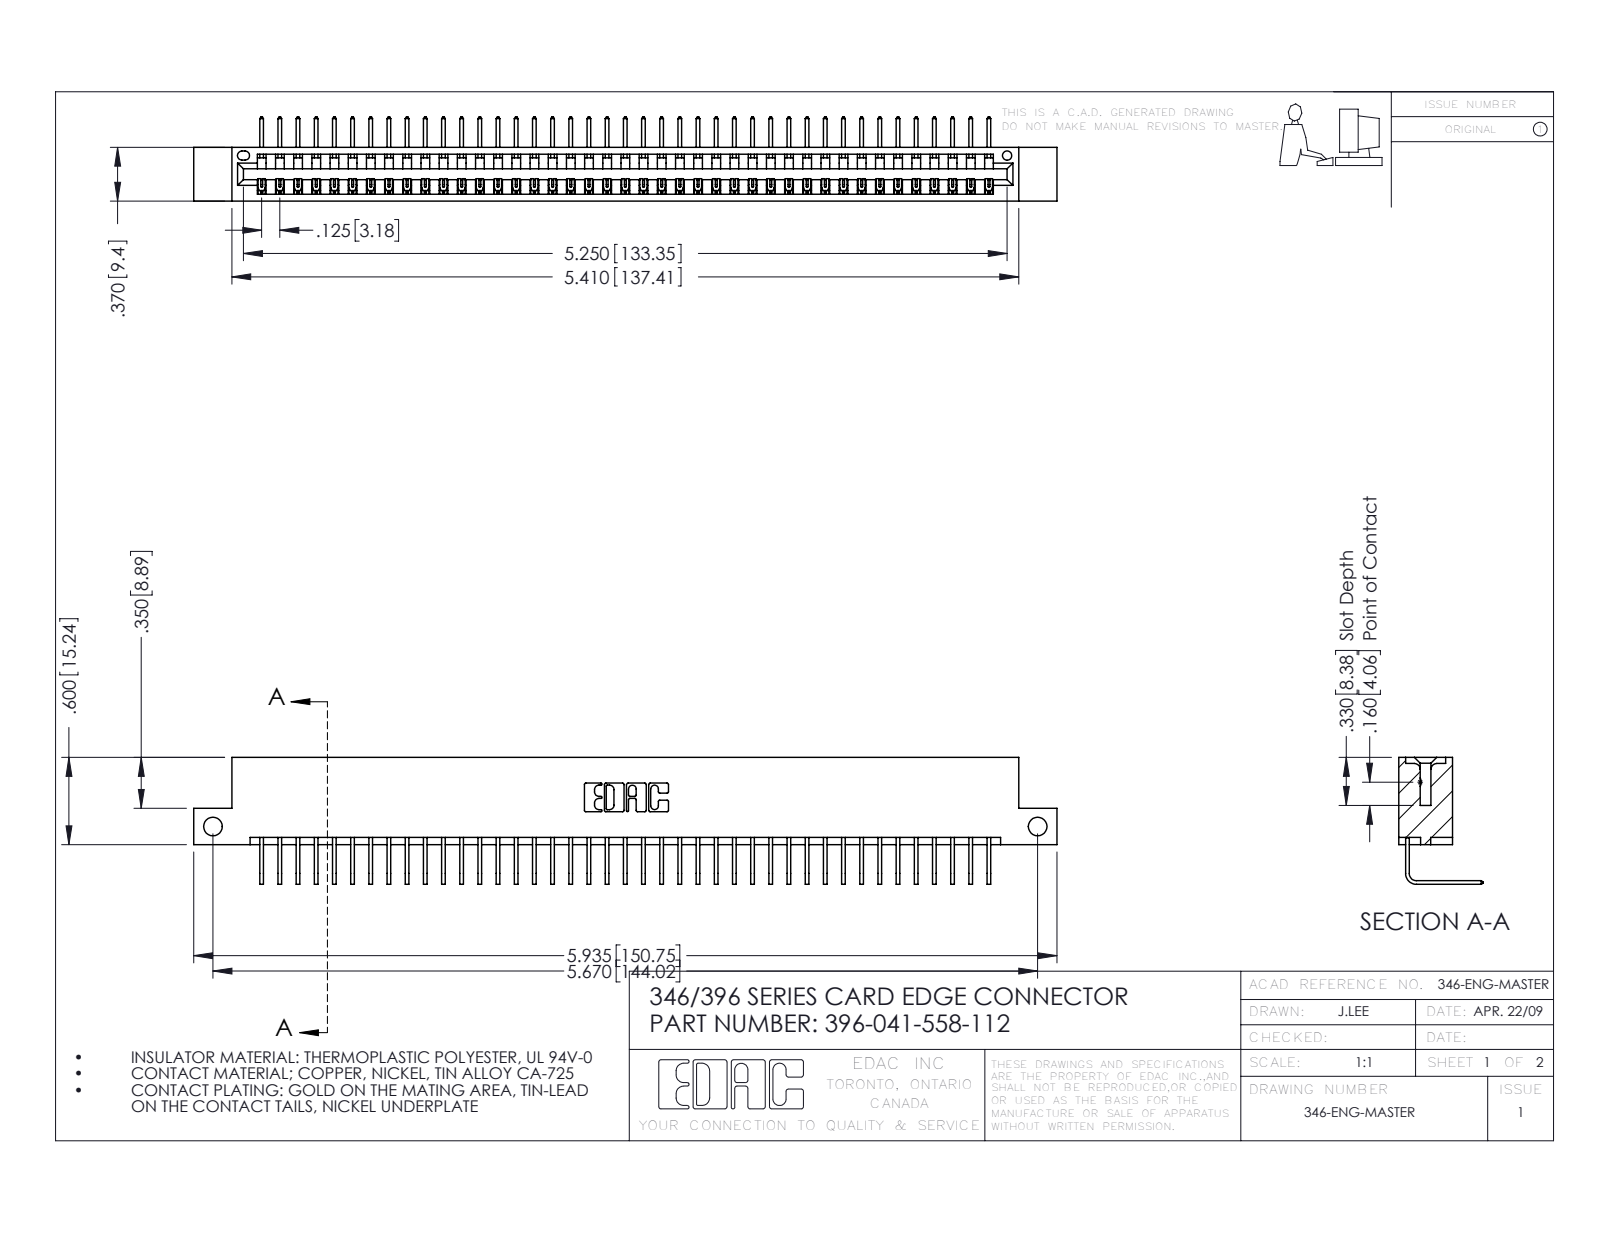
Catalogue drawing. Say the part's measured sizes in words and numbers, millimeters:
The part is named "345-292-001_558 Tail - 2; 346 Part_Flush Mounting Lugs - Side Mount; 396-041-558-112". Its 3-D file was written by "SolidWorks 2016 (CONFIG_CONTROL_DESIGN)". It is 42 solids with 2582 faces: 1798 planar, 784 cylindrical and 0 other. Overall it measures 150.7 by 22.2 by 14.7 millimeters. Its volume is 14 500 cubic millimeters and its surface area 18 750 square millimeters. Round holes: 2 of diameter 3.3, 1 of diameter 1.6. Partial cylindrical surfaces (rounded edges, fillets, slot ends): 82 of radius 0.2, 22 of radius 0.3, 6 of radius 0.2, 6 of radius 0.8, 3 of radius 0.7, 2 of radius 0.8, 2 of radius 1, 1 of radius 0.4. The main face-to-face distances are 8.2, 1.2, 9.4, 6.4, 7.6, 0.6, 1.8, 3.8, 5.6, 2.5. The hole center spacings are 144.
